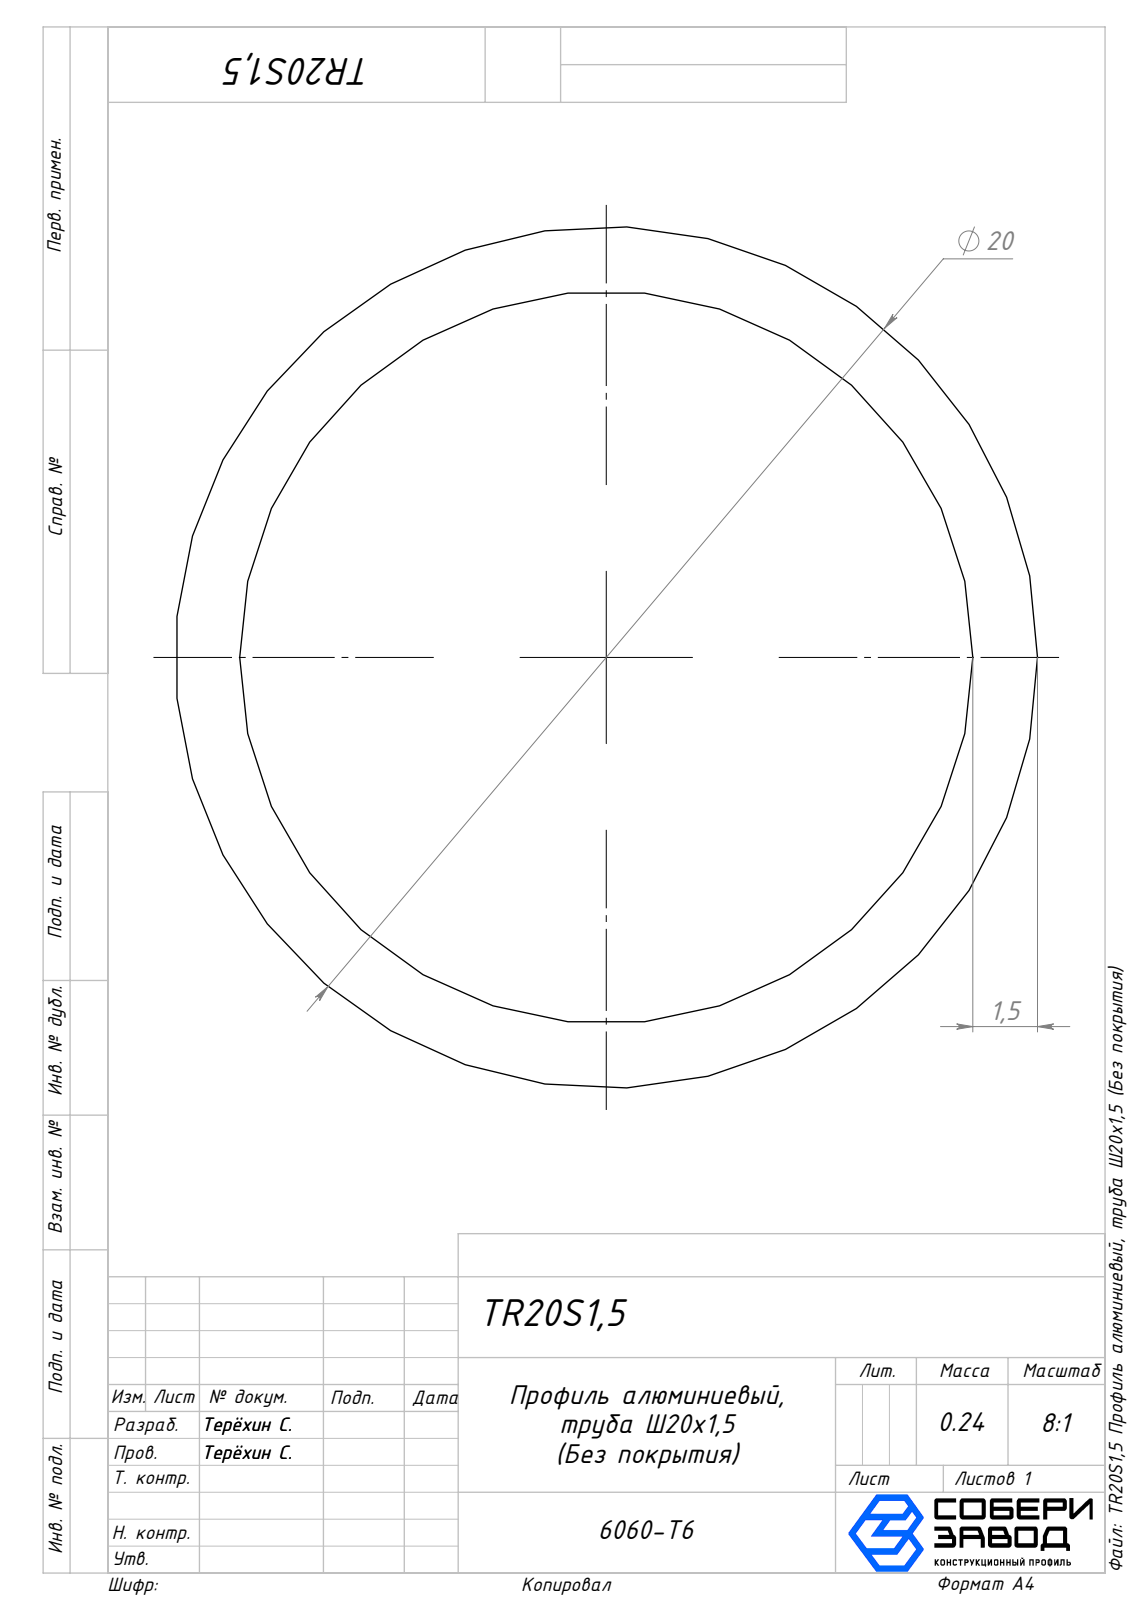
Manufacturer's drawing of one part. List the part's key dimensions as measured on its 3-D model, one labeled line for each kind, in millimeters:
Part name (STEP PRODUCT): Сборка10; TR20S1,5 Профиль алюминиевый, труба Ø20х1,5 (Без покрытия)_00
STEP written by: SolidWorks 2025 (AUTOMOTIVE_DESIGN)
Units: millimetres
Bodies: 1 solid, 6 faces (2 planar, 4 cylindrical, 0 other)
Overall size (bounding box): 1000 × 20 × 20
Volume: 87 179 mm³ · Surface area: 116 413 mm²
Round holes (diameter × count): ⌀17 ×1
Round bosses / shafts (diameter × count): ⌀20 ×1
Main face-to-face distances: 1000
